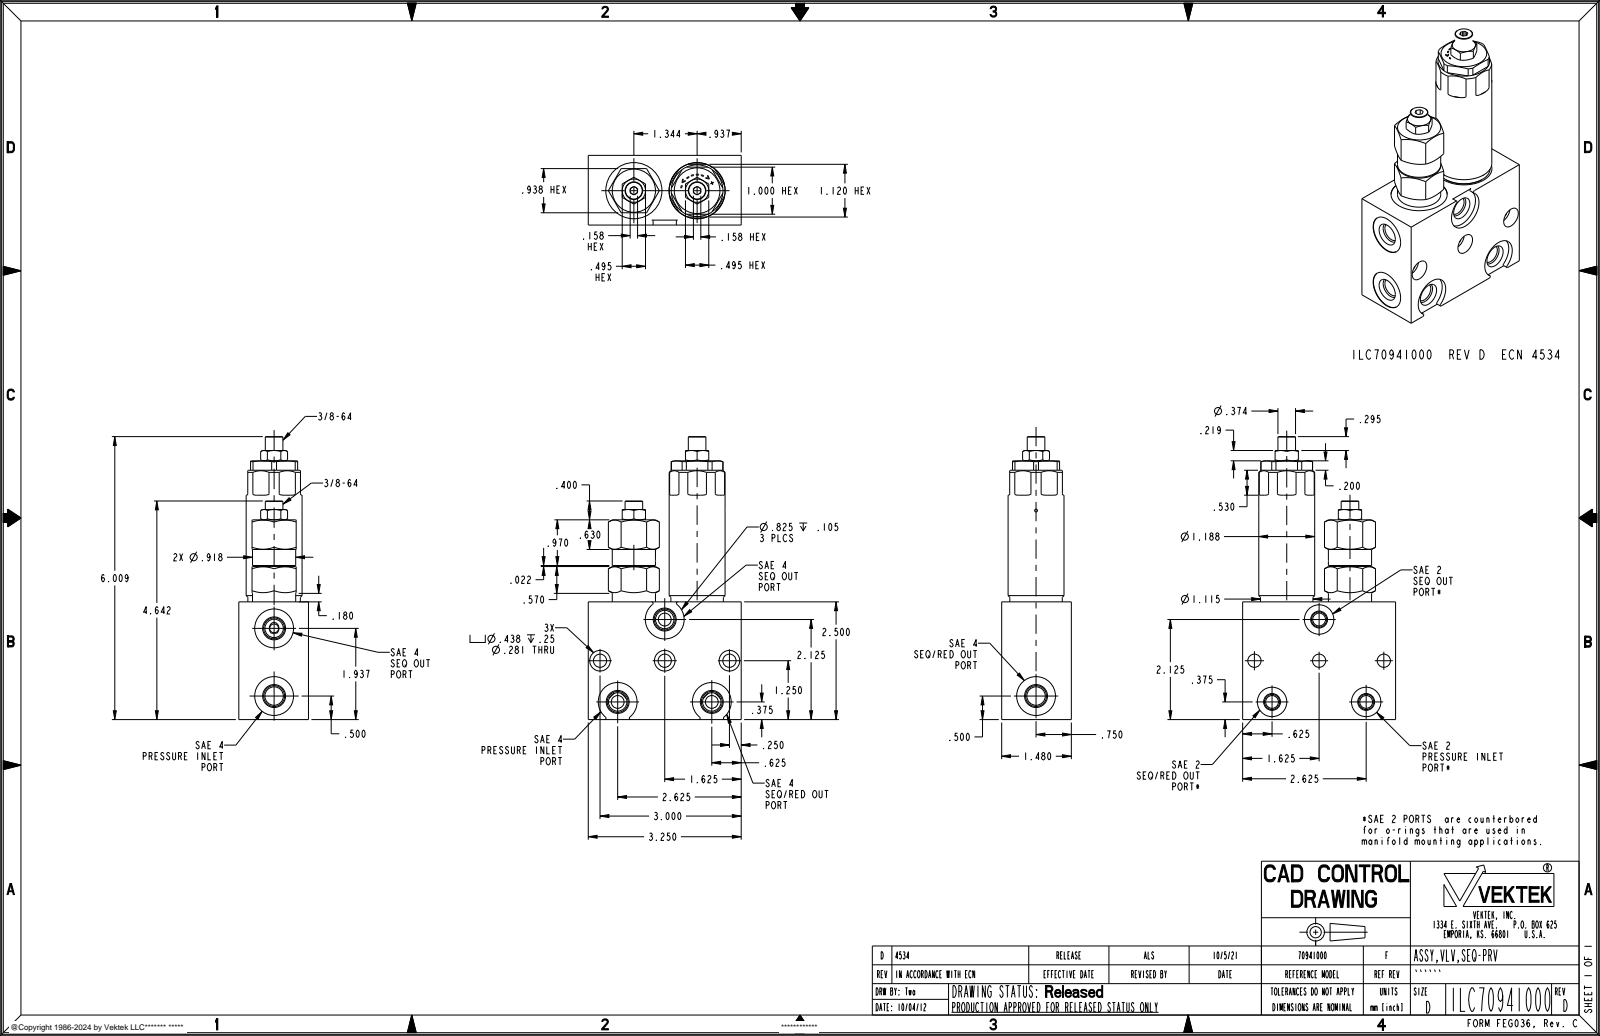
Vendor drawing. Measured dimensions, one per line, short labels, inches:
name: ILC70941000
written by: PRO/ENGINEER BY PARAMETRIC TECHNOLOGY CORPORATION, 2017170 (AUTOMOTIVE_DESIGN)
unit: in
bodies: 2 solids, 789 faces (260 planar, 274 cylindrical, 255 other)
size: 6.191 × 3.25 × 1.514
volume: 13.61 in³; area: 96.22 in²
holes: 7× ⌀0.392, 4× ⌀0.063, 4× ⌀0.272, 4× ⌀0.625, 3× ⌀0.047, 3× ⌀0.281, 3× ⌀0.438, 2× ⌀0.019, 2× ⌀0.078, 2× ⌀0.094, 2× ⌀0.125, 2× ⌀0.188
bosses: 2× ⌀0.374, 1× ⌀1.188, 1× ⌀1.115, 1× ⌀0.918, 1× ⌀0.8, 1× ⌀0.695, 1× ⌀0.684, 1× ⌀0.67
rounds: 12× R0.03, 8× R0.005, 3× R0.412, 2× R0.014, 2× R0.021, 1× R0.123, 1× R0.152, 1× R0.177
face distances: 1.48, 3.25, 2.5, 3.24, 0.938, 1.375, 0.105, 2.49, 0.281, 1.219
hole spacings: 0.21, 0.297, 0.42, 0.952, 1.329, 1.36, 2.531, 3.263
